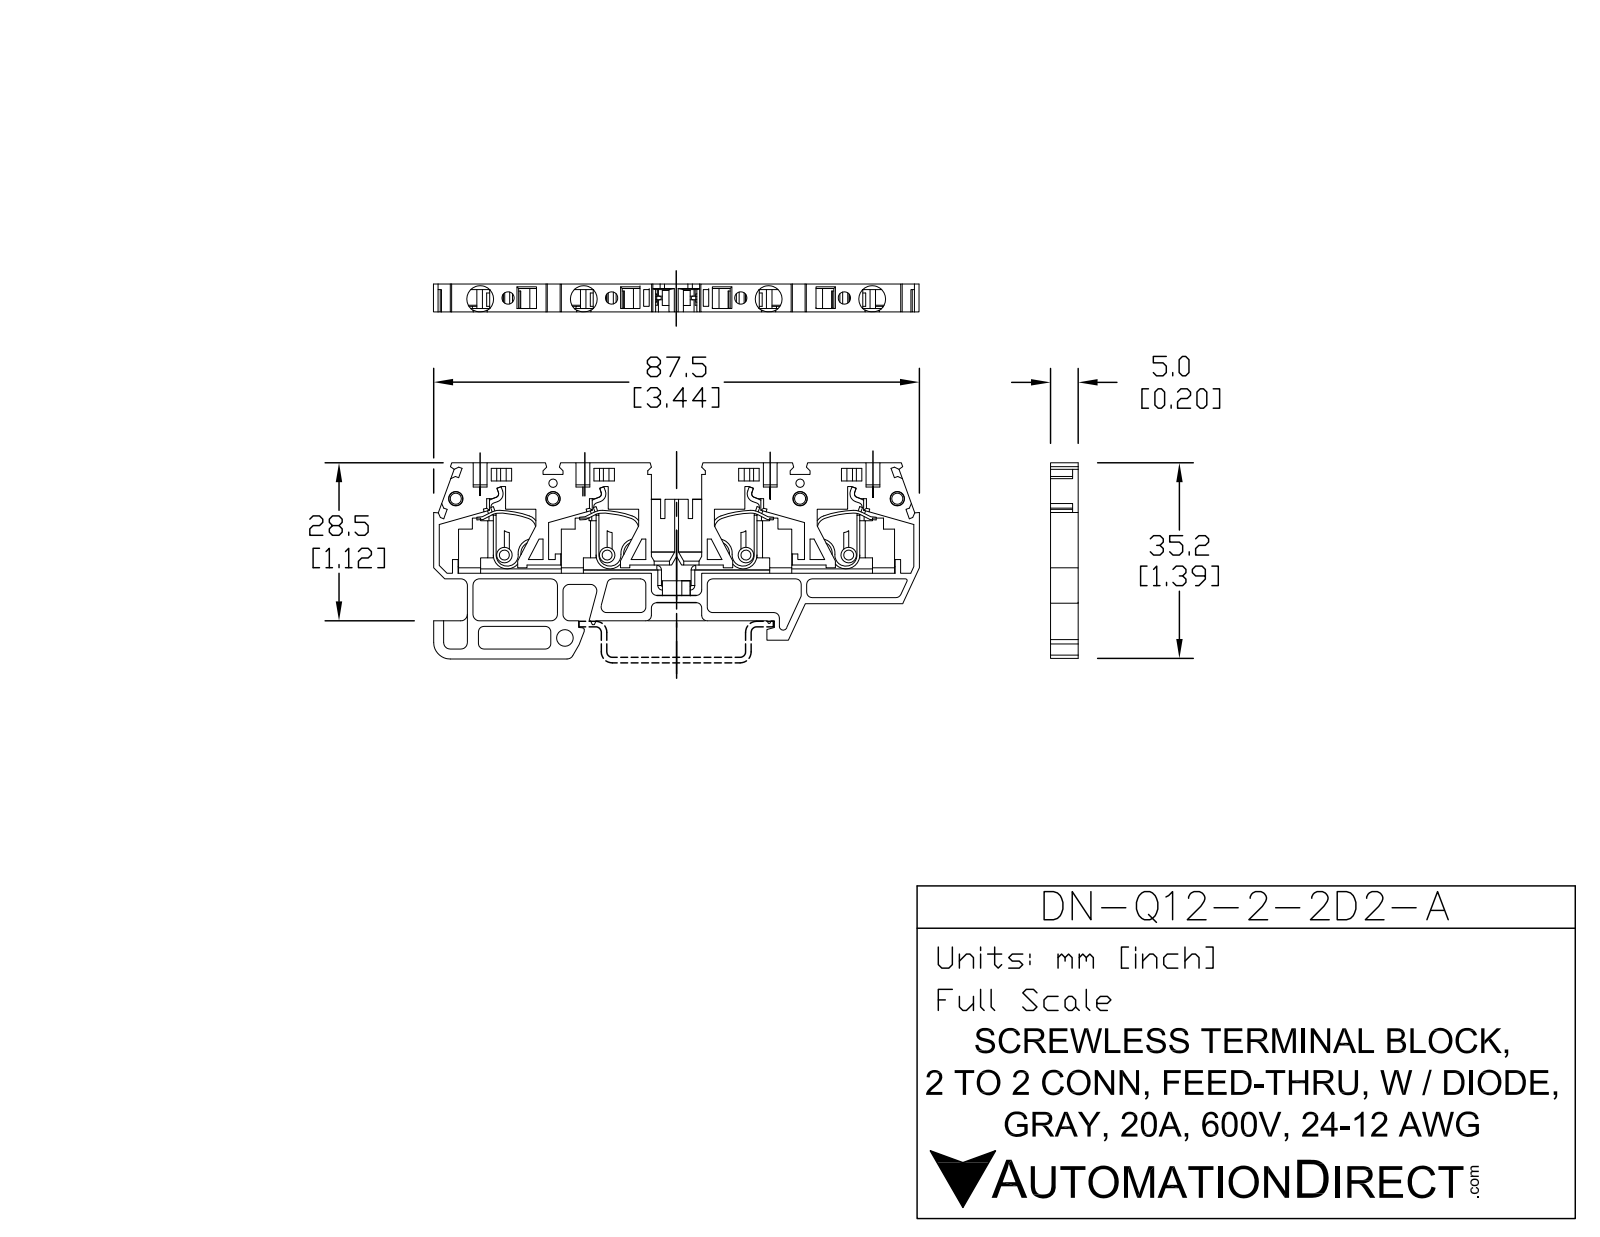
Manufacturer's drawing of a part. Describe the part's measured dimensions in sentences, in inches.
The part is named "20310_Piega3; 42414D1_DN-Q12-2-2D2-A; 42414_DN-Q12-2-2-A". Its 3-D file was written by "SolidWorks 2013 (AUTOMOTIVE_DESIGN)". It is 1 solid with 478 faces: 332 planar, 104 cylindrical and 42 other. Overall it measures 3.433 by 1.394 by 0.197 inches. Its volume is 0.505 cubic inches and its surface area 13.6 square inches. Round holes: 4 of diameter 0.087, 4 of diameter 0.102, 4 of diameter 0.189, 2 of diameter 0.059, 1 of diameter 0.118. Round bosses or shafts: 3 of diameter 0.024, 1 of diameter 0.106. Partial cylindrical surfaces (rounded edges, fillets, slot ends): 22 of radius 0.039, 12 of radius 0.047, 2 of radius 0.012, 1 of radius 0.028, 1 of radius 0.118. The main face-to-face distances are 0.197, 0.039, 0.079, 0.118, 0.331, 0.173, 0.047, 0.295, 0.031, 1.122. The hole center spacings are 0.197, 0.732, 1.843, 0.11, 0.535, 0.693, 0.702, 0.929.
